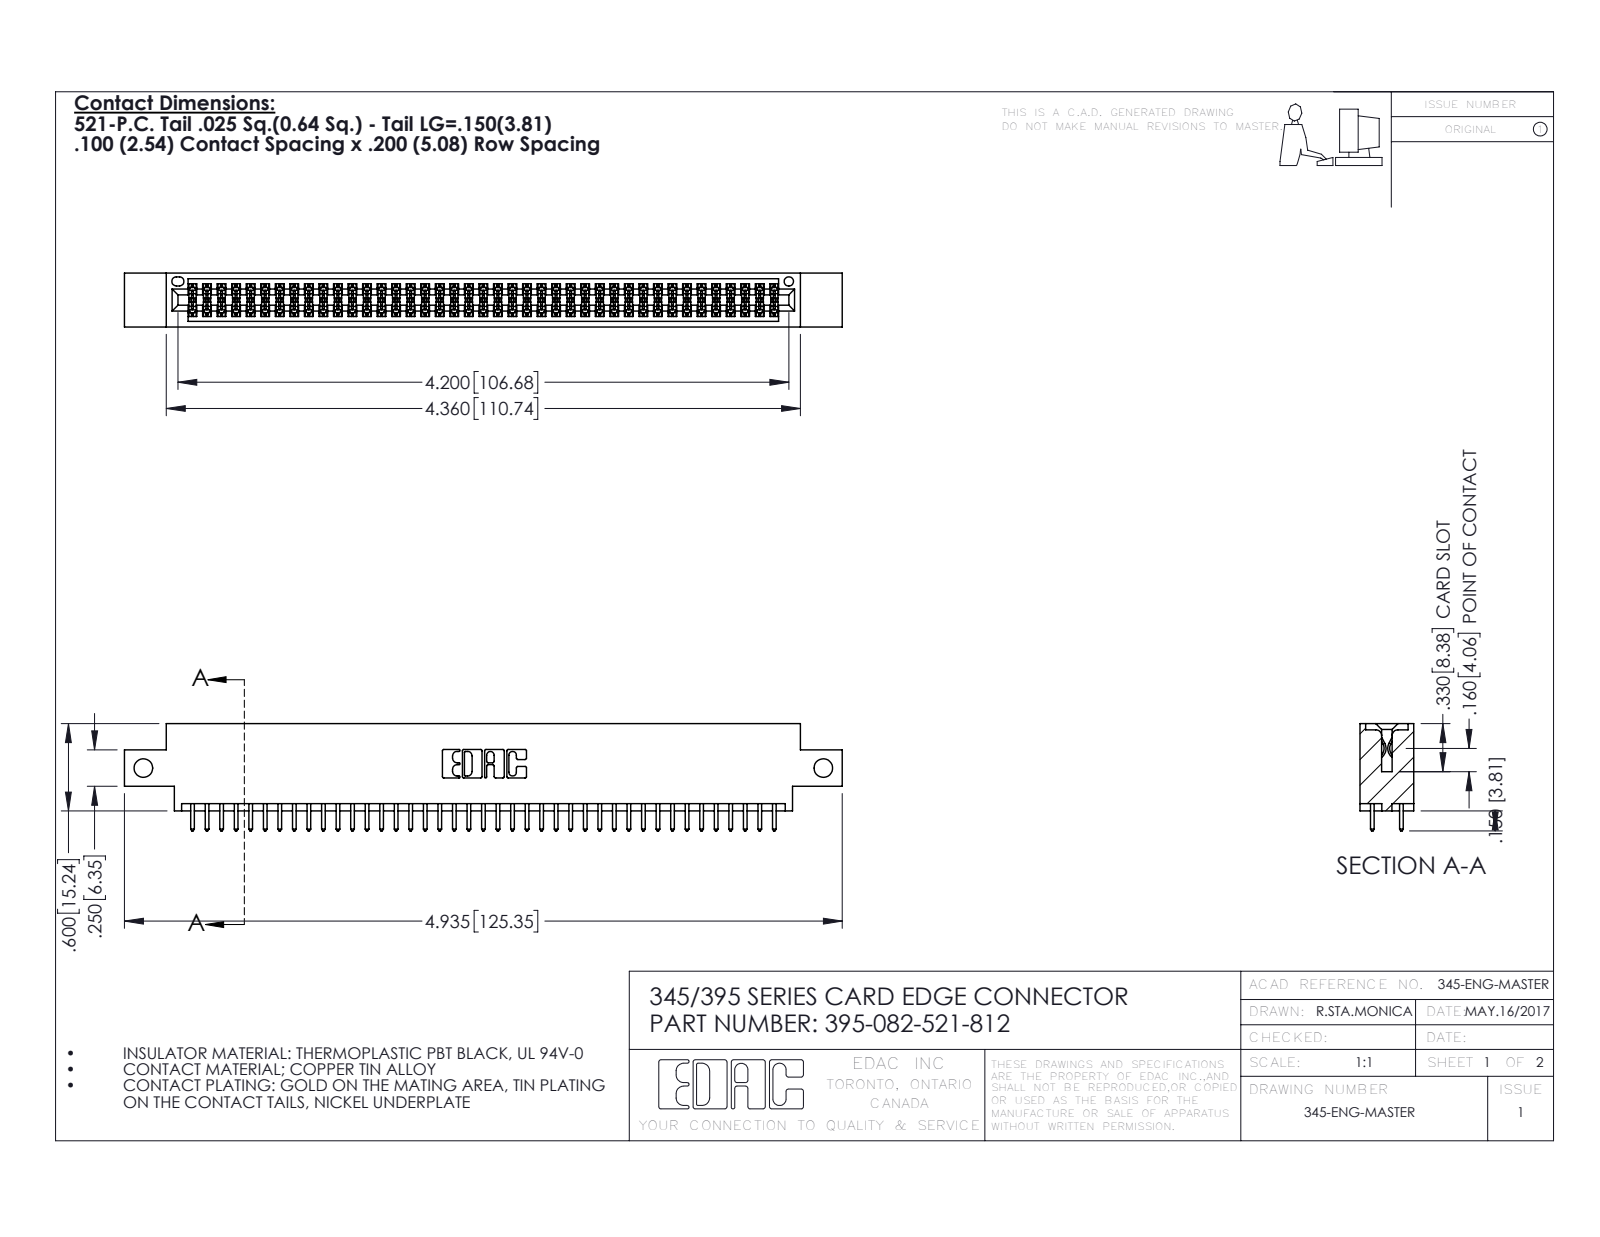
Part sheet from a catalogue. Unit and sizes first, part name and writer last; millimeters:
Units: millimetres
Overall size (bounding box): 125.3 × 18.7 × 9.4
Round holes (diameter × count): ⌀3.3 ×2, ⌀1.6 ×1
Partial cylindrical surfaces — rounded edges, fillets, slot ends (radius × count): R0.2 ×123, R0.3 ×82, R0.3 ×22, R0.2 ×6, R0.8 ×6, R0.7 ×3, R0.4 ×2, R0.5 ×2
Main face-to-face distances: 7.6, 1.8, 9.4, 5.1, 2.5, 6.9, 0.6, 5.7, 4.4, 3.8
Hole centre spacings: 118.7
Volume: 11 900 mm³ · Surface area: 17 410 mm²
Bodies: 83 solids, 4230 faces (2790 planar, 1440 cylindrical, 0 other)
Part name (STEP PRODUCT): 345 Part_0.170 Offset - Side Mount; 345-292-001_345-293-121; 395-082-521-812
STEP written by: SolidWorks 2016 (CONFIG_CONTROL_DESIGN)
